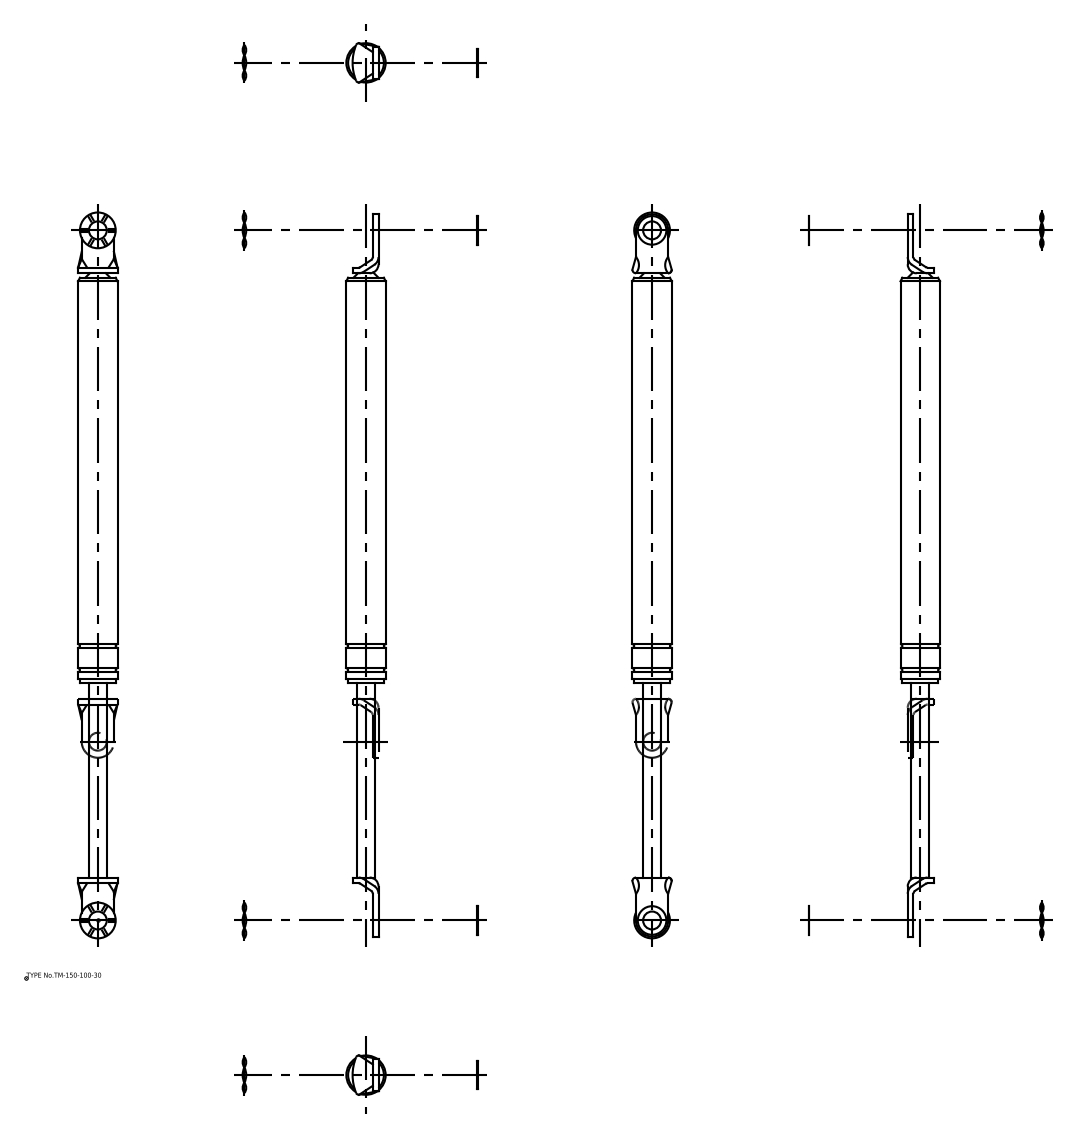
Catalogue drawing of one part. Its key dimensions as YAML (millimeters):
part_name: "ウェーブワッシャー; ワッシャー; 本体; 本体_div"
step_written_by: "spGate 16.7.1 (AUTOMOTIVE_DESIGN)"
units: millimeters
bodies: {solids: 6, faces: 94, planar: 42, cylindrical: 44, other: 8}
overall_size: [406, 22.5, 22.5]
volume: 100374
surface_area: 25534
round_holes:
  - {diameter: 10, count: 2}
round_bosses_or_shafts:
  - {diameter: 20, count: 3}
  - {diameter: 16, count: 2}
  - {diameter: 22.5, count: 1}
  - {diameter: 22, count: 1}
  - {diameter: 10, count: 1}
partial_cylinders:
  - {radius: 4.4, count: 2}
  - {radius: 5, count: 2}
  - {radius: 9, count: 2}
  - {radius: 26.32, count: 1}
face_to_face_distances: [3.2, 2, 5.2, 341.2, 5.7, 3.7, 0.5, 232.2, 112.2, 344.4]
hole_center_spacings: [386]
